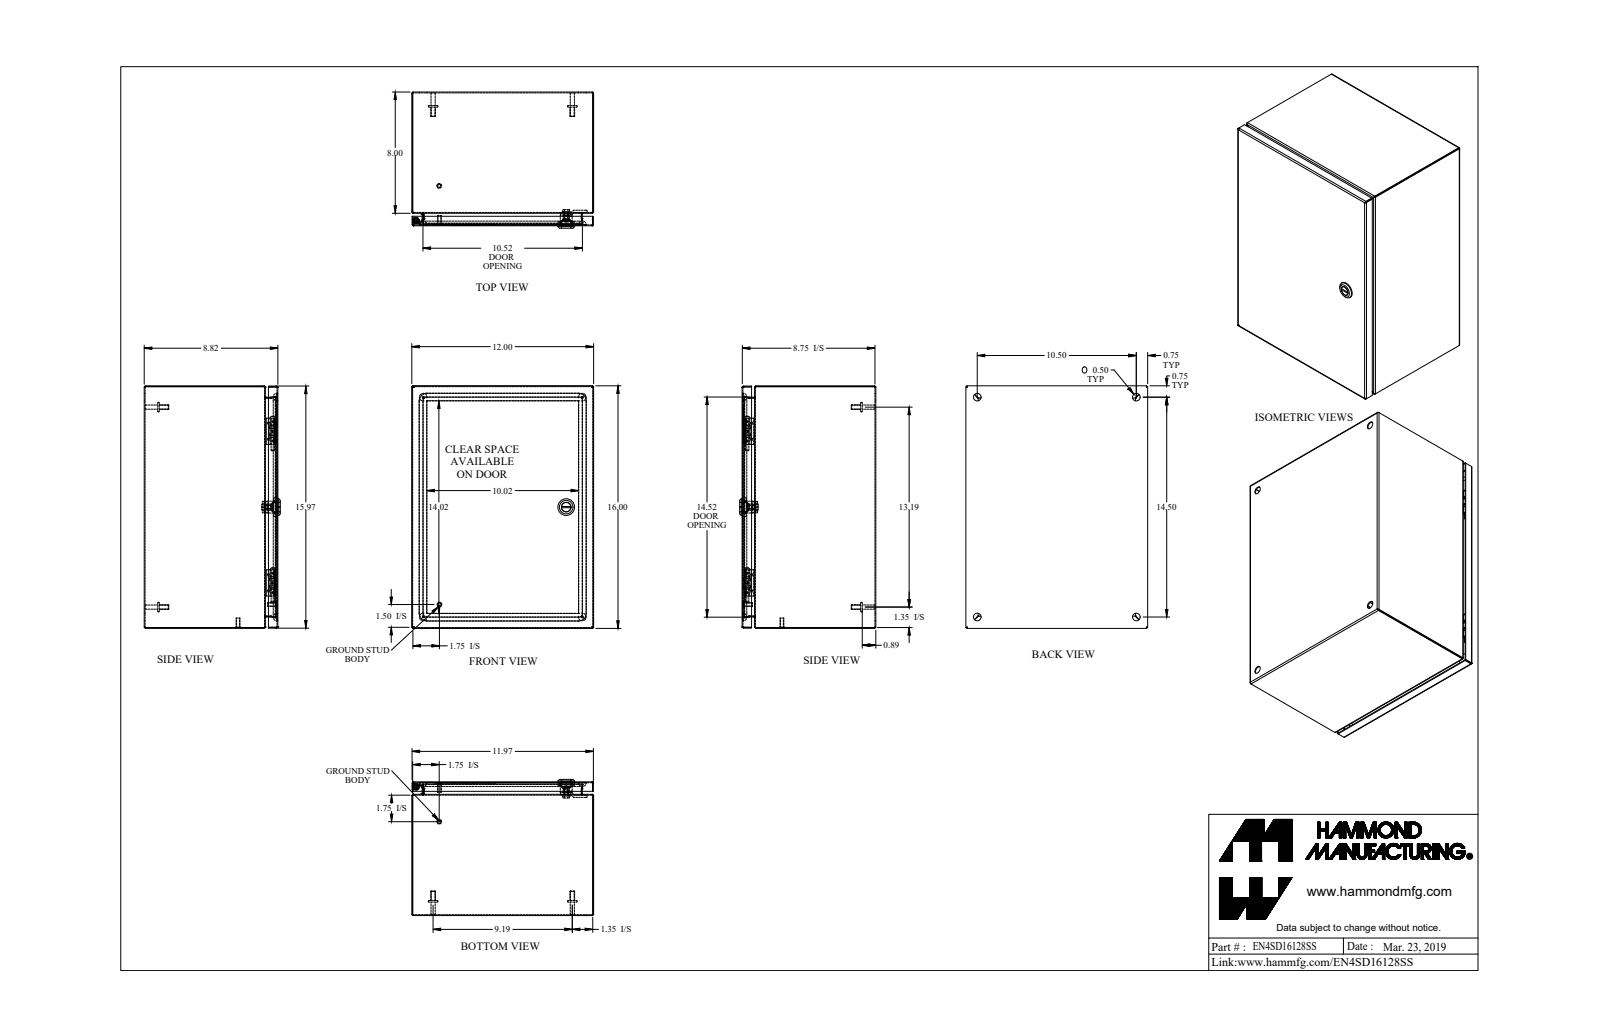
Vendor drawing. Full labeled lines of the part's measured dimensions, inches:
Part name (STEP PRODUCT): EN4SD16128SS_Default
STEP written by: SolidWorks 2019 (CONFIG_CONTROL_DESIGN)
Units: inches
Bodies: 20 solids, 639 faces (301 planar, 204 cylindrical, 134 other)
Overall size (bounding box): 16 × 12 × 8.982
Volume: 59.31 in³ · Surface area: 2 009 in²
Round holes (diameter × count): ⌀0.5 ×5, ⌀0.197 ×1, ⌀0.24 ×1, ⌀0.242 ×1, ⌀0.387 ×1, ⌀0.63 ×1, ⌀0.768 ×1
Round bosses / shafts (diameter × count): ⌀0.313 ×6, ⌀0.625 ×5, ⌀0.275 ×4, ⌀0.25 ×2, ⌀1.1 ×1, ⌀0.785 ×1, ⌀0.525 ×1, ⌀0.455 ×1
Partial cylindrical surfaces — rounded edges, fillets, slot ends (radius × count): R0.029 ×21, R0.086 ×21, R0.188 ×12, R0.006 ×4, R0.062 ×4, R0.25 ×4, R0.499 ×4, R0.125 ×2
Main face-to-face distances: 0.057, 8.765, 11.943, 8.708, 8.822, 15.943, 11.886, 12, 15.886, 16
Hole centre spacings: 7.327, 10.5, 11.904, 14.5, 17.902
